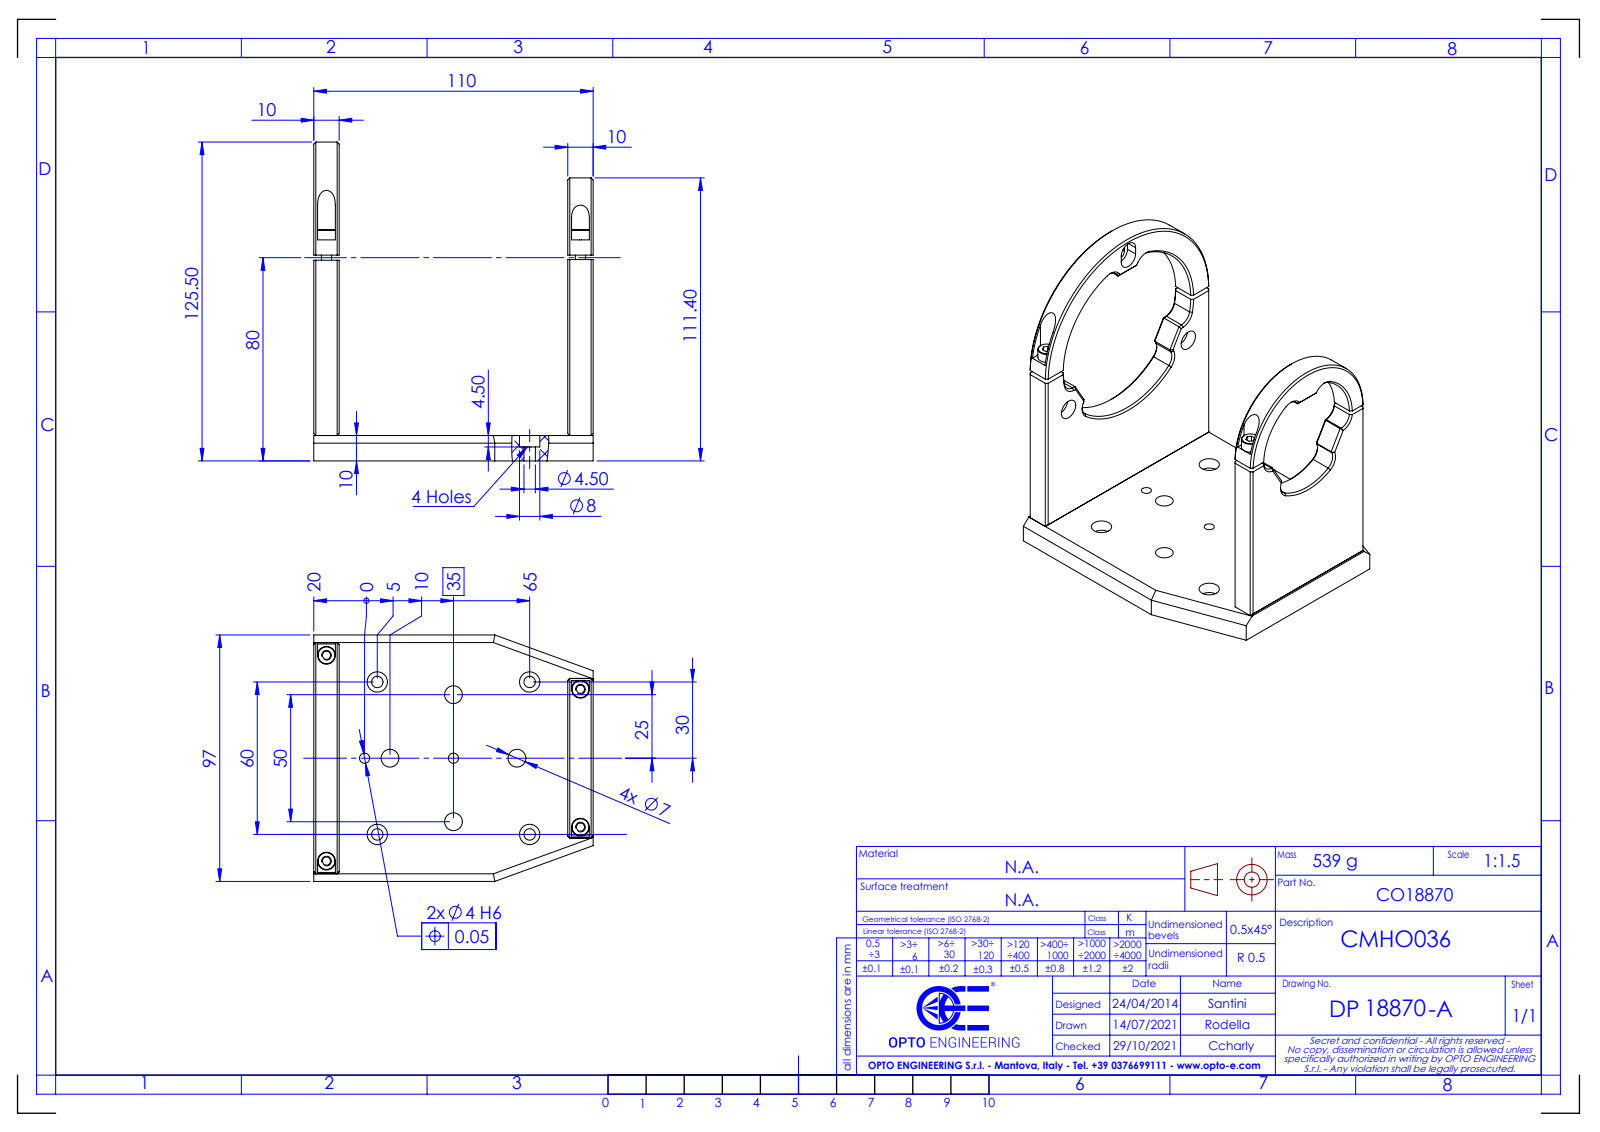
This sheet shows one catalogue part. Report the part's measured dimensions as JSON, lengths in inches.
{"part_name": "DP18870-A_CMHO036", "step_written_by": "SolidWorks 2021 (CONFIG_CONTROL_DESIGN)", "units": "inches", "bodies": {"solids": 0, "faces": 321, "planar": 163, "cylindrical": 94, "other": 64}, "overall_size": [4.941, 4.331, 3.819], "round_holes": [[0.315, 10], [0.177, 6], [0.276, 6], [0.157, 2]], "round_bosses_or_shafts": [[0.276, 4], [0.157, 2]], "partial_cylinders_radius": [[0.197, 12], [0.089, 2], [0.157, 2], [0.941, 1], [1.236, 1], [1.398, 1], [1.791, 1]], "face_to_face_distances": [0.394, 3.937, 4.331, 3.543, 0.555, 3.028, 0.118, 0.673, 3.146, 3.701], "hole_center_spacings": [1.197, 2.467, 1.392, 2.362, 1.969, 0.984, 1.67, 0.787]}
